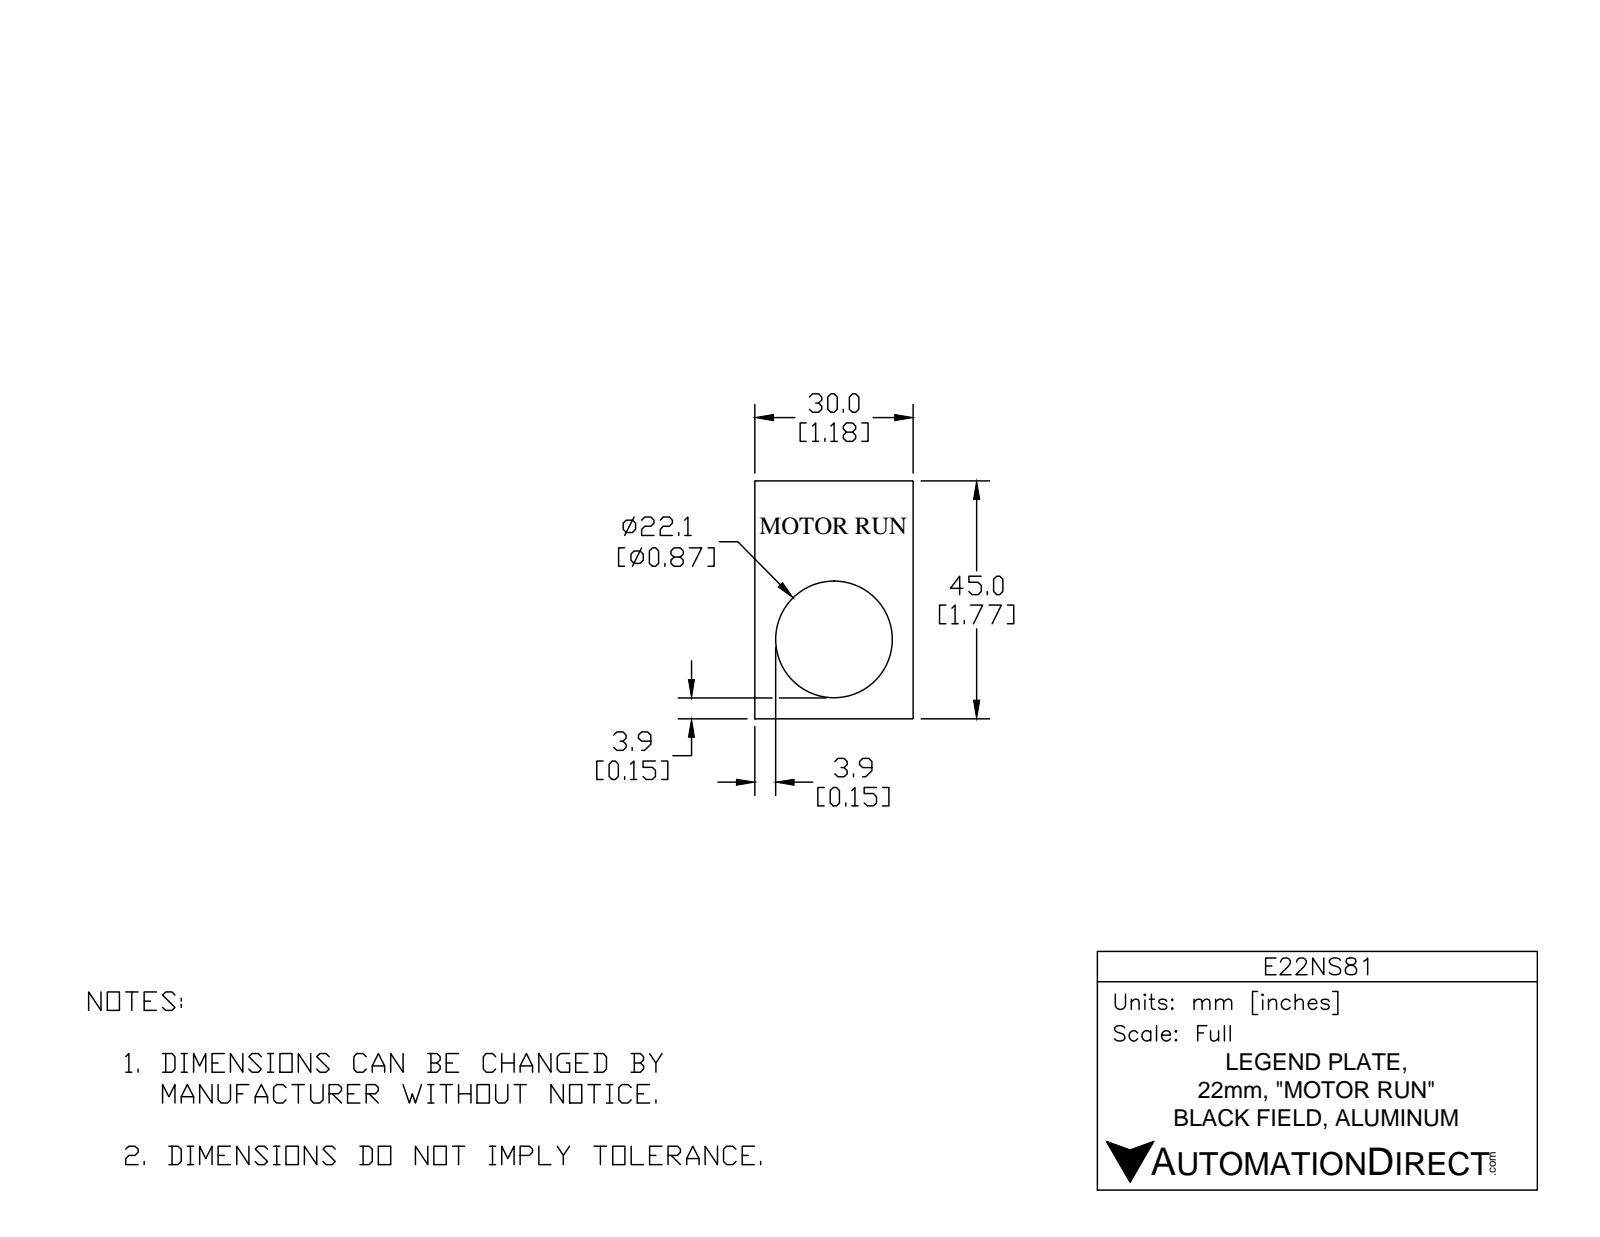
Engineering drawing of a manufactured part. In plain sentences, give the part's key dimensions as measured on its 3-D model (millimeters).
The part is named "E22NS81". Its 3-D file was written by "SolidWorks 2017 (AUTOMOTIVE_DESIGN)". It is 1 solid with 116 faces: 80 planar, 3 cylindrical and 33 other. Overall it measures 45 by 30 by 1.3 millimeters. Its volume is 1 250 cubic millimeters and its surface area 2 253 square millimeters. Round holes: 1 of diameter 22.2. The main face-to-face distances are 1.3, 30, 45, 1.05, 4.7, 40.3, 16.6, 5.29, 13.4, 11.6.
